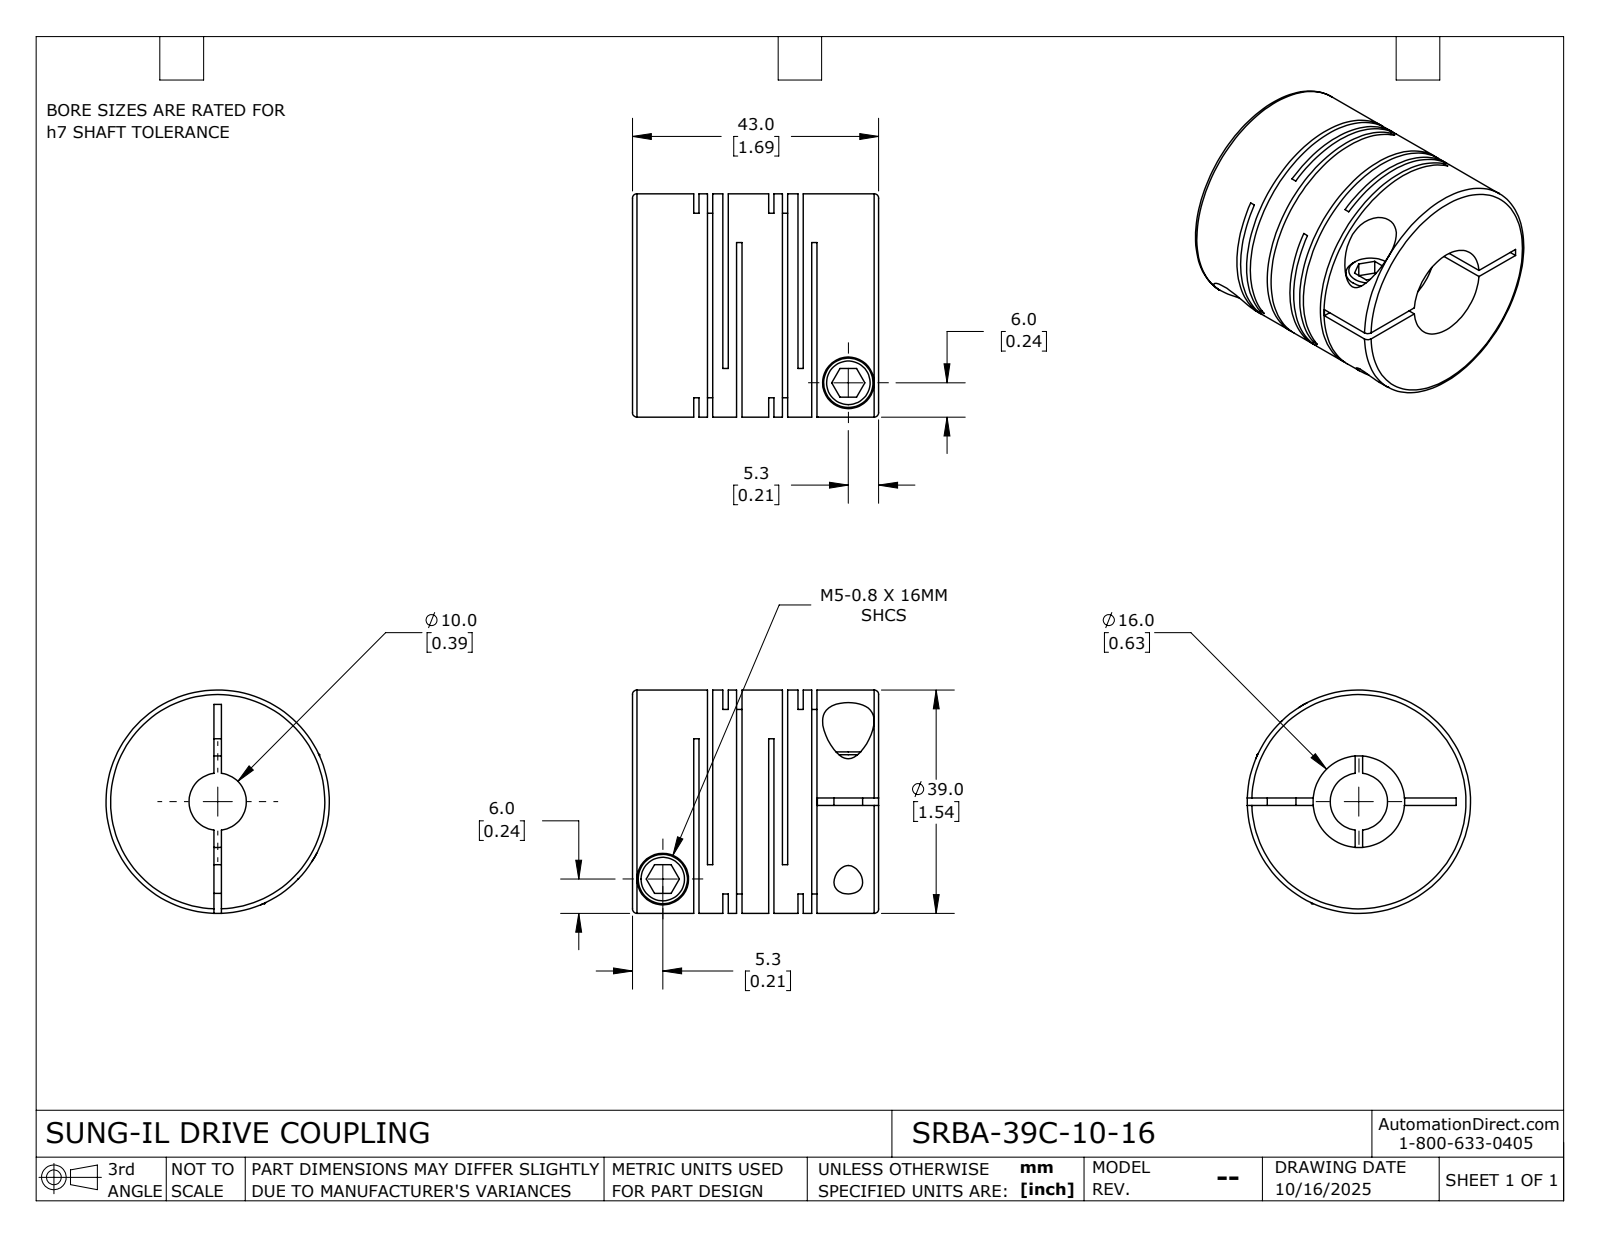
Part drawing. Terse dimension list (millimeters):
name: SRBA-39C-10-16
written by: SolidWorks 2024 (CONFIG_CONTROL_DESIGN)
unit: mm
bodies: 1 solid, 115 faces (60 planar, 42 cylindrical, 13 other)
size: 43 × 39 × 39
volume: 36 590 mm³; area: 23 103 mm²
holes: 2× ⌀5, 2× ⌀9, 1× ⌀10, 1× ⌀16
bosses: 2× ⌀8.6, 1× ⌀39
face distances: 13.1, 0.92, 2.4, 5.1, 10.7, 14.02, 18.2, 12.18, 3.32, 7.5
